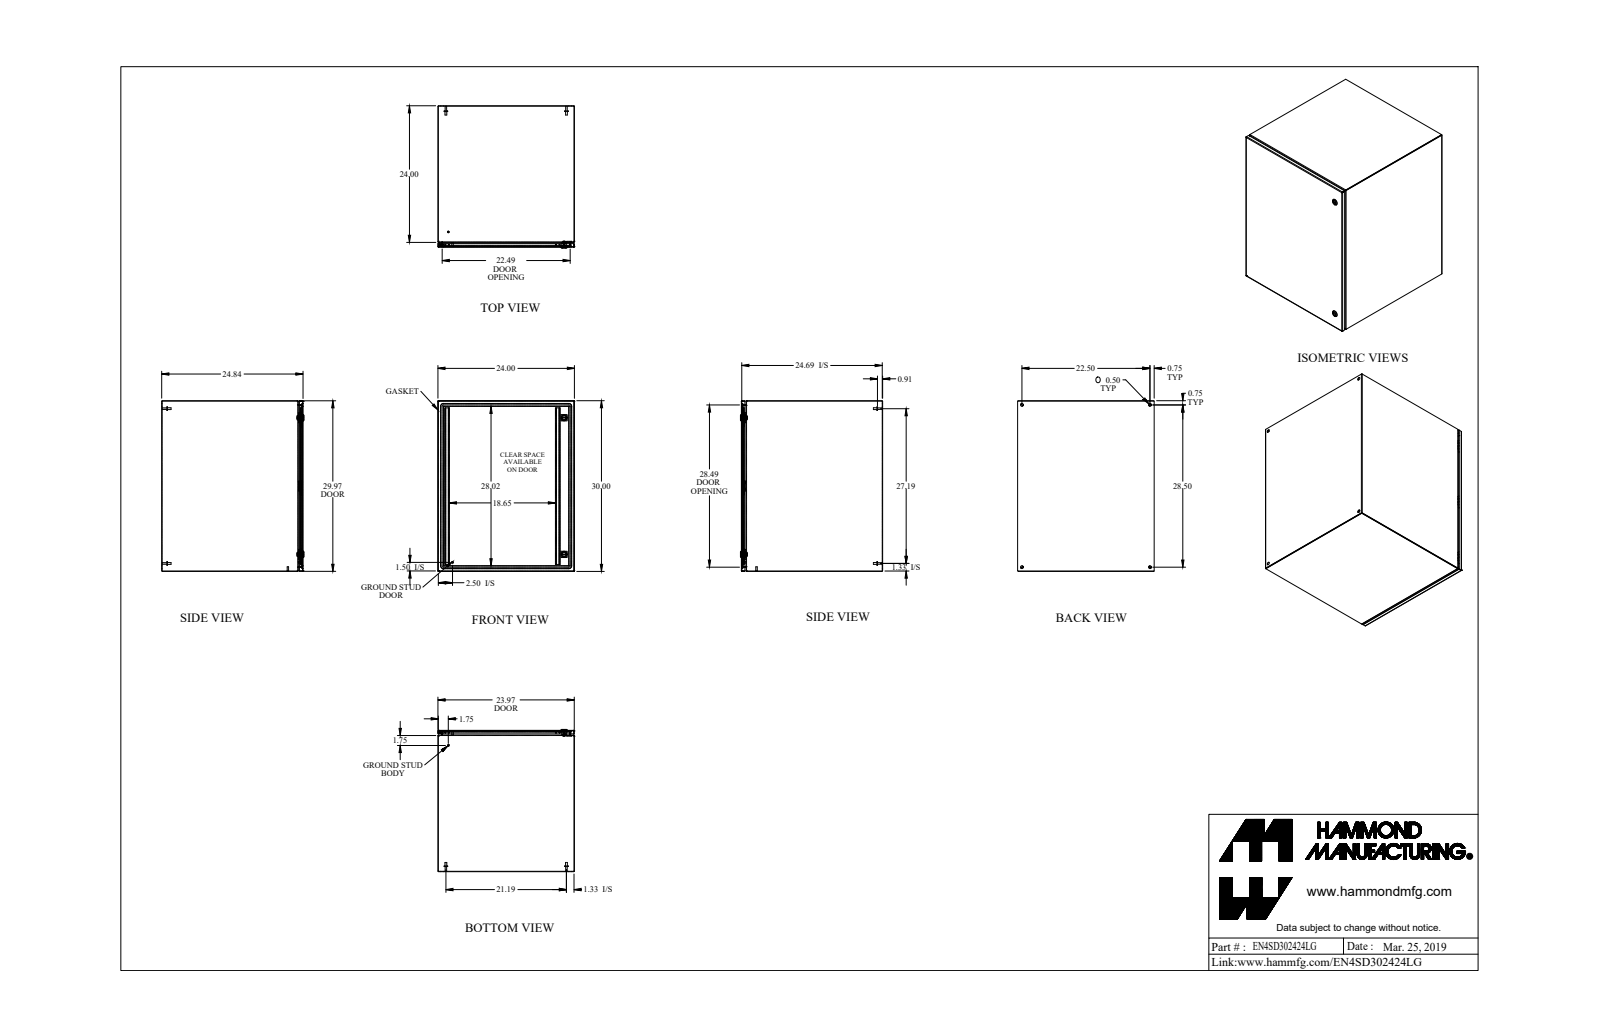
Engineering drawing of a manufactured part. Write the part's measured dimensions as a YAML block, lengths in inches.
part_name: "EN4SD302424LG"
step_written_by: "SolidWorks 2019 (AUTOMOTIVE_DESIGN)"
units: inches
bodies: {solids: 33, faces: 838, planar: 399, cylindrical: 283, other: 156}
overall_size: [30, 24.997, 24]
volume: 319.1
surface_area: 8937
round_holes:
  - {diameter: 0.5, count: 4}
  - {diameter: 0.232, count: 2}
  - {diameter: 0.625, count: 2}
  - {diameter: 0.785, count: 2}
  - {diameter: 0.172, count: 1}
  - {diameter: 0.24, count: 1}
  - {diameter: 0.242, count: 1}
round_bosses_or_shafts:
  - {diameter: 0.625, count: 4}
  - {diameter: 0.313, count: 4}
  - {diameter: 0.27, count: 4}
  - {diameter: 1.1, count: 2}
  - {diameter: 0.525, count: 2}
  - {diameter: 0.281, count: 2}
  - {diameter: 0.25, count: 2}
  - {diameter: 0.455, count: 1}
partial_cylinders:
  - {radius: 0.036, count: 14}
  - {radius: 0.108, count: 14}
  - {radius: 0.043, count: 12}
  - {radius: 0.081, count: 12}
  - {radius: 0.312, count: 12}
  - {radius: 0.1, count: 8}
  - {radius: 0.006, count: 6}
  - {radius: 0.062, count: 6}
face_to_face_distances: [0.072, 23.928, 24.765, 29.928, 23.856, 24, 24.693, 24.837, 29.856, 30]
hole_center_spacings: [22.5, 28.5, 36.311, 2.493, 2.494, 21.545, 21.545, 23.999]
